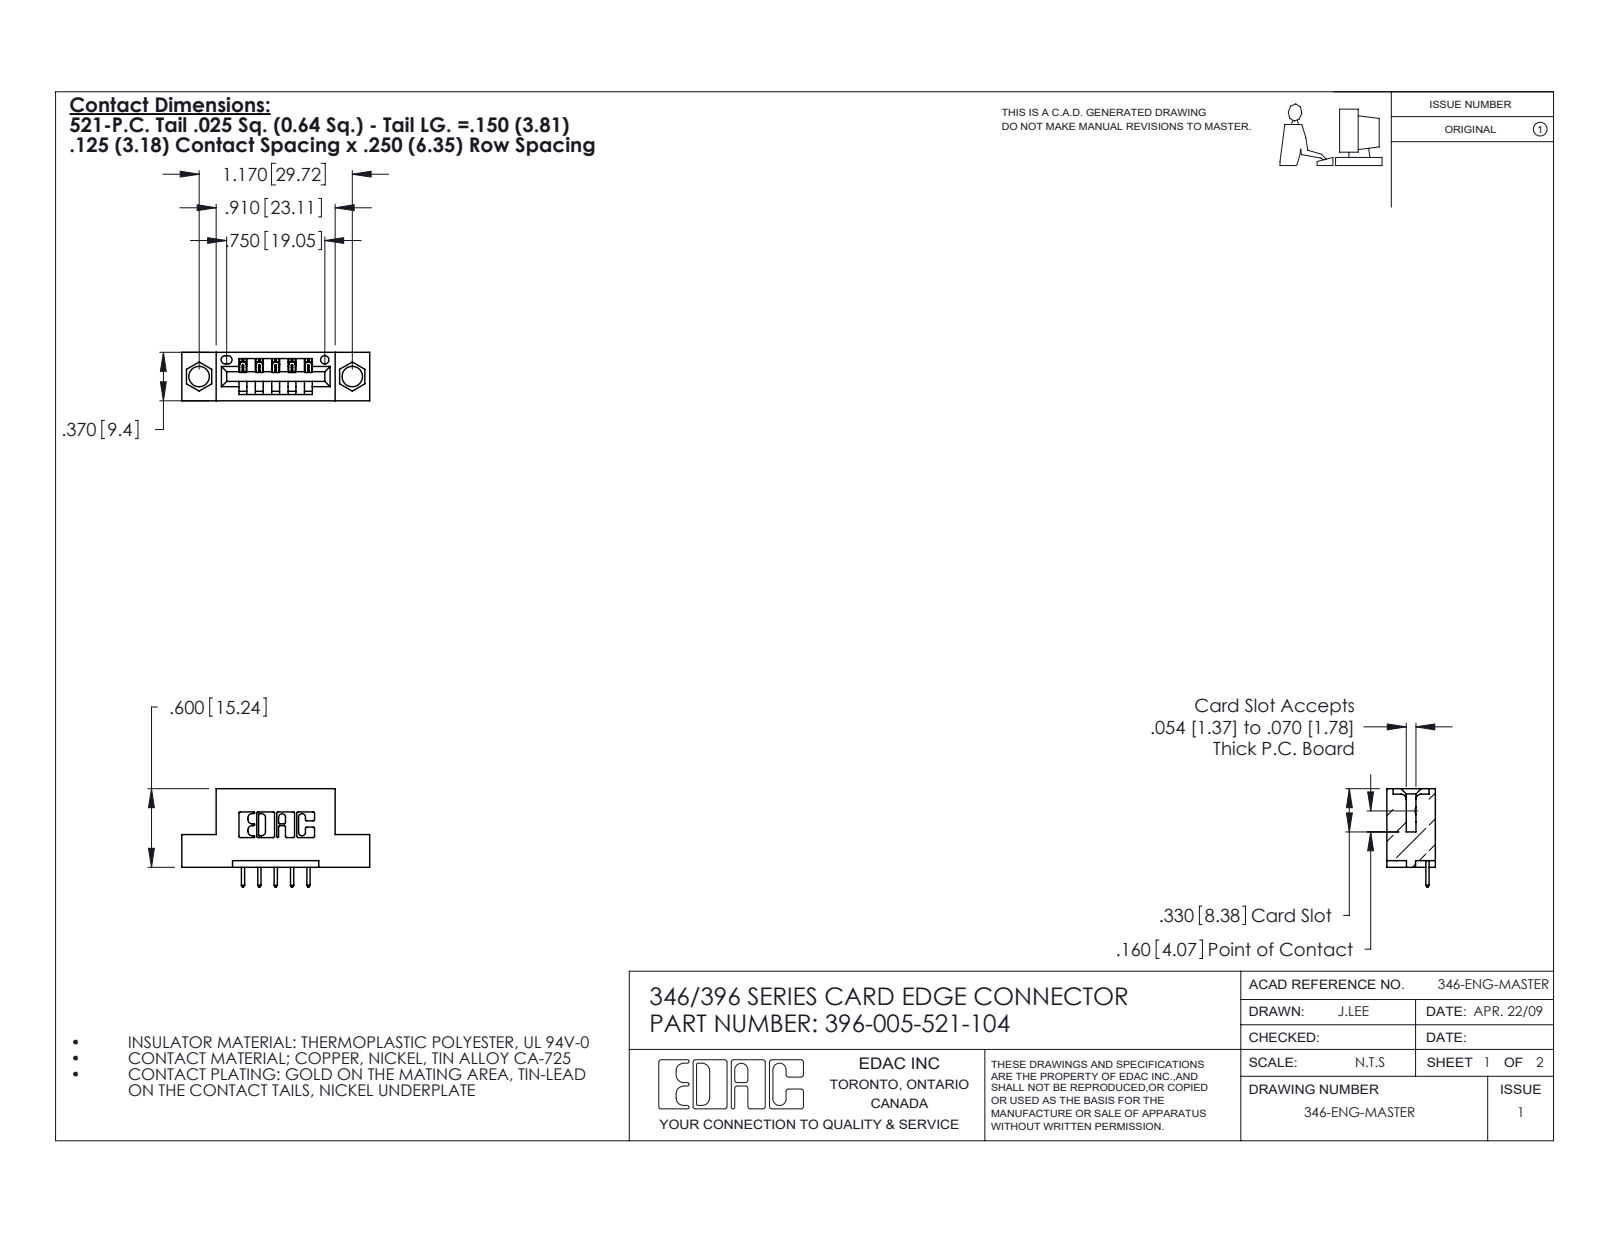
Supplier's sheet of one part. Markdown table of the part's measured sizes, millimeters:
| quantity | value |
| --- | --- |
| part name | 345-292-001_345-293-121; 346 Part_Flush Mounting Lugs - 0.156 Dia-TH; 396-005-521-104 |
| STEP written by | SolidWorks 2020 (CONFIG_CONTROL_DESIGN) |
| units | millimeters |
| bodies | 6 solids, 426 faces (290 planar, 136 cylindrical, 0 other) |
| overall size | 36.4 × 19.1 × 9.4 |
| volume | 3 110 mm³ |
| surface area | 3 274 mm² |
| round holes (diameter × count) | 4 × 2, 1.6 × 1 |
| partial cylindrical surfaces (radius × count) | 0.3 × 22, 0.2 × 10, 0.3 × 10, 0.2 × 6, 0.8 × 6, 0.7 × 3, 0.8 × 2, 1 × 2 |
| main face-to-face distances | 6.4, 9.4, 1.2, 8.2, 3.8, 5.6, 2.5, 4.4, 14, 3.2 |
| hole center spacings | 6.2, 24.6, 29.7 |
